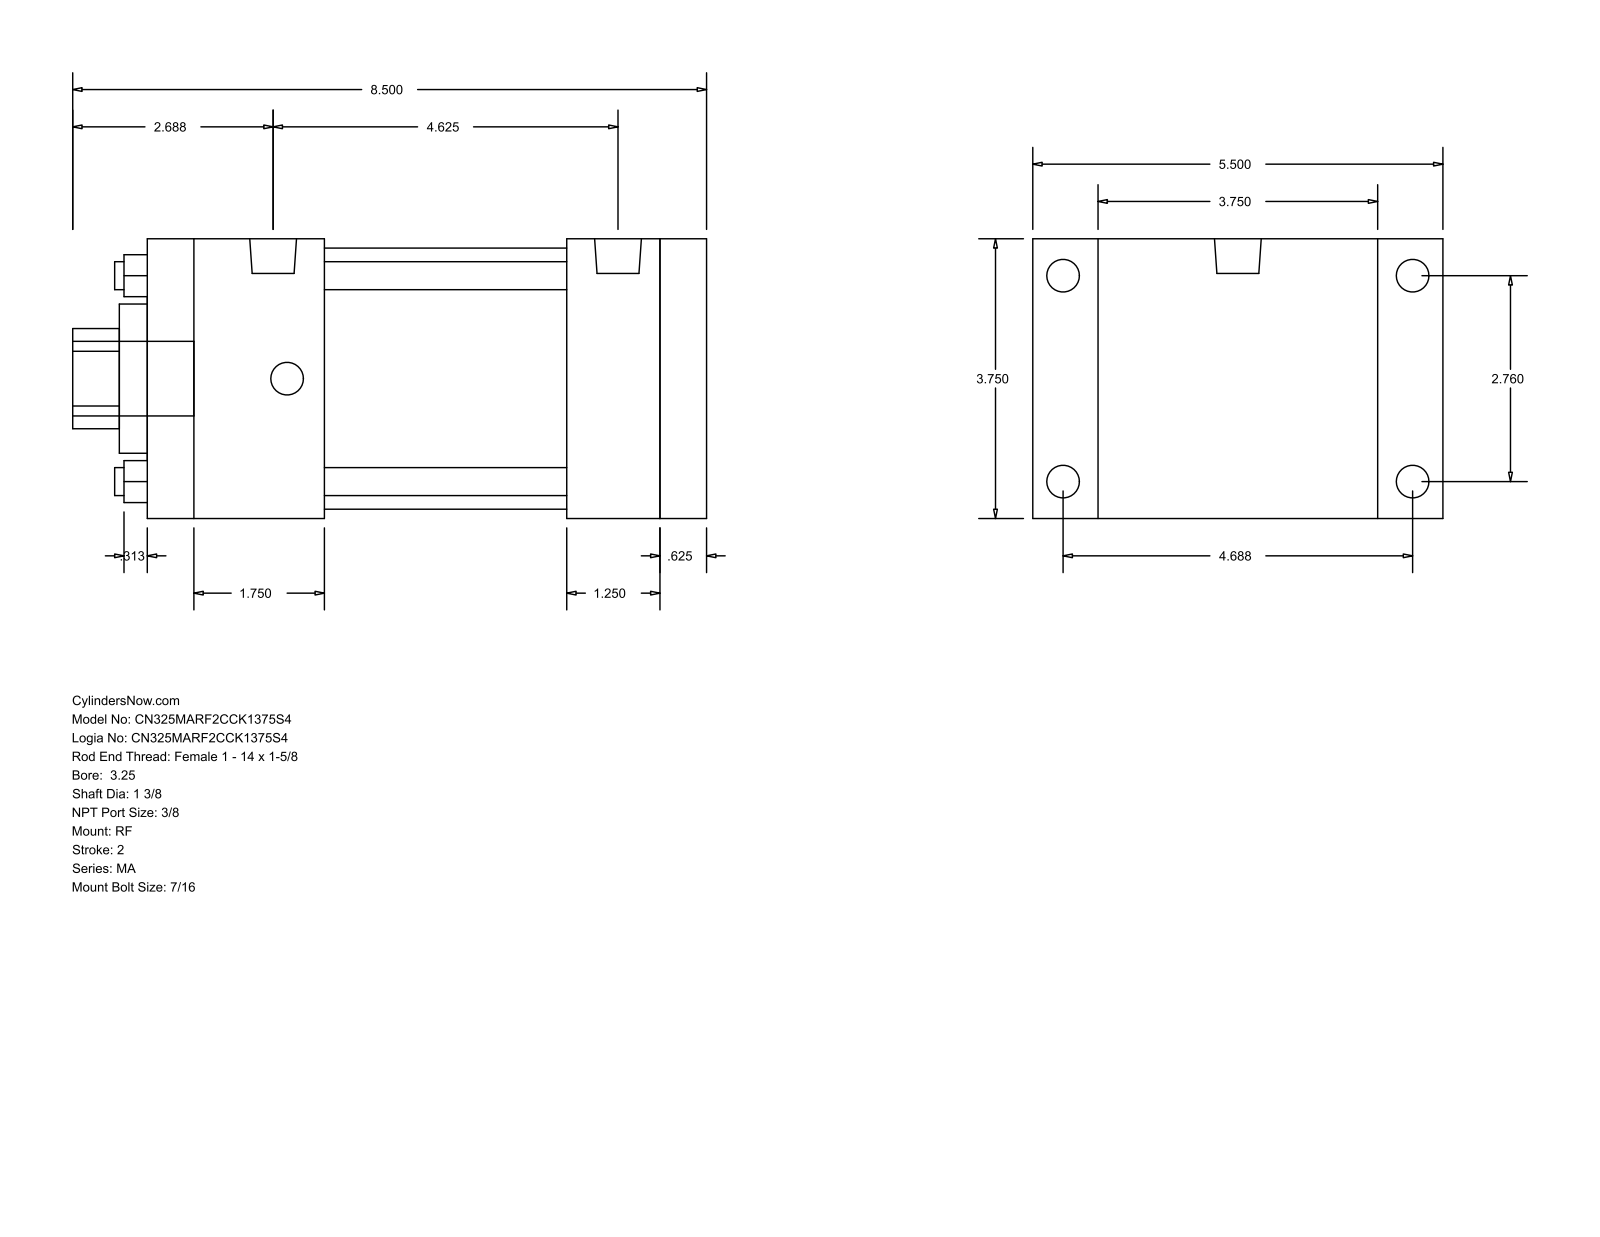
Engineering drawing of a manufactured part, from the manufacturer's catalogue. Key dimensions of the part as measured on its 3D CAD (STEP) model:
Part name (STEP PRODUCT): MA_RF__0325_1.375
STEP written by: GSSL Pune (CONFIG_CONTROL_DESIGN)
Units: millimetres
Bodies: 0 solids, 92 faces (64 planar, 28 cylindrical, 0 other)
Overall size (bounding box): 215.9 × 139.7 × 95.25
Round holes (diameter × count): ⌀9.53 ×4, ⌀34.92 ×1, ⌀50.8 ×1, ⌀88.9 ×1
Round bosses / shafts (diameter × count): ⌀11.11 ×8, ⌀15.93 ×2, ⌀25.4 ×1
Partial cylindrical surfaces — rounded edges, fillets, slot ends (radius × count): R17.06 ×1
Main face-to-face distances: 95.24, 190.5, 15.87, 174.63, 22.23, 117.47, 142.88, 31.75, 47.62, 60.32
Hole centre spacings: 49.57, 70.1, 99.14
